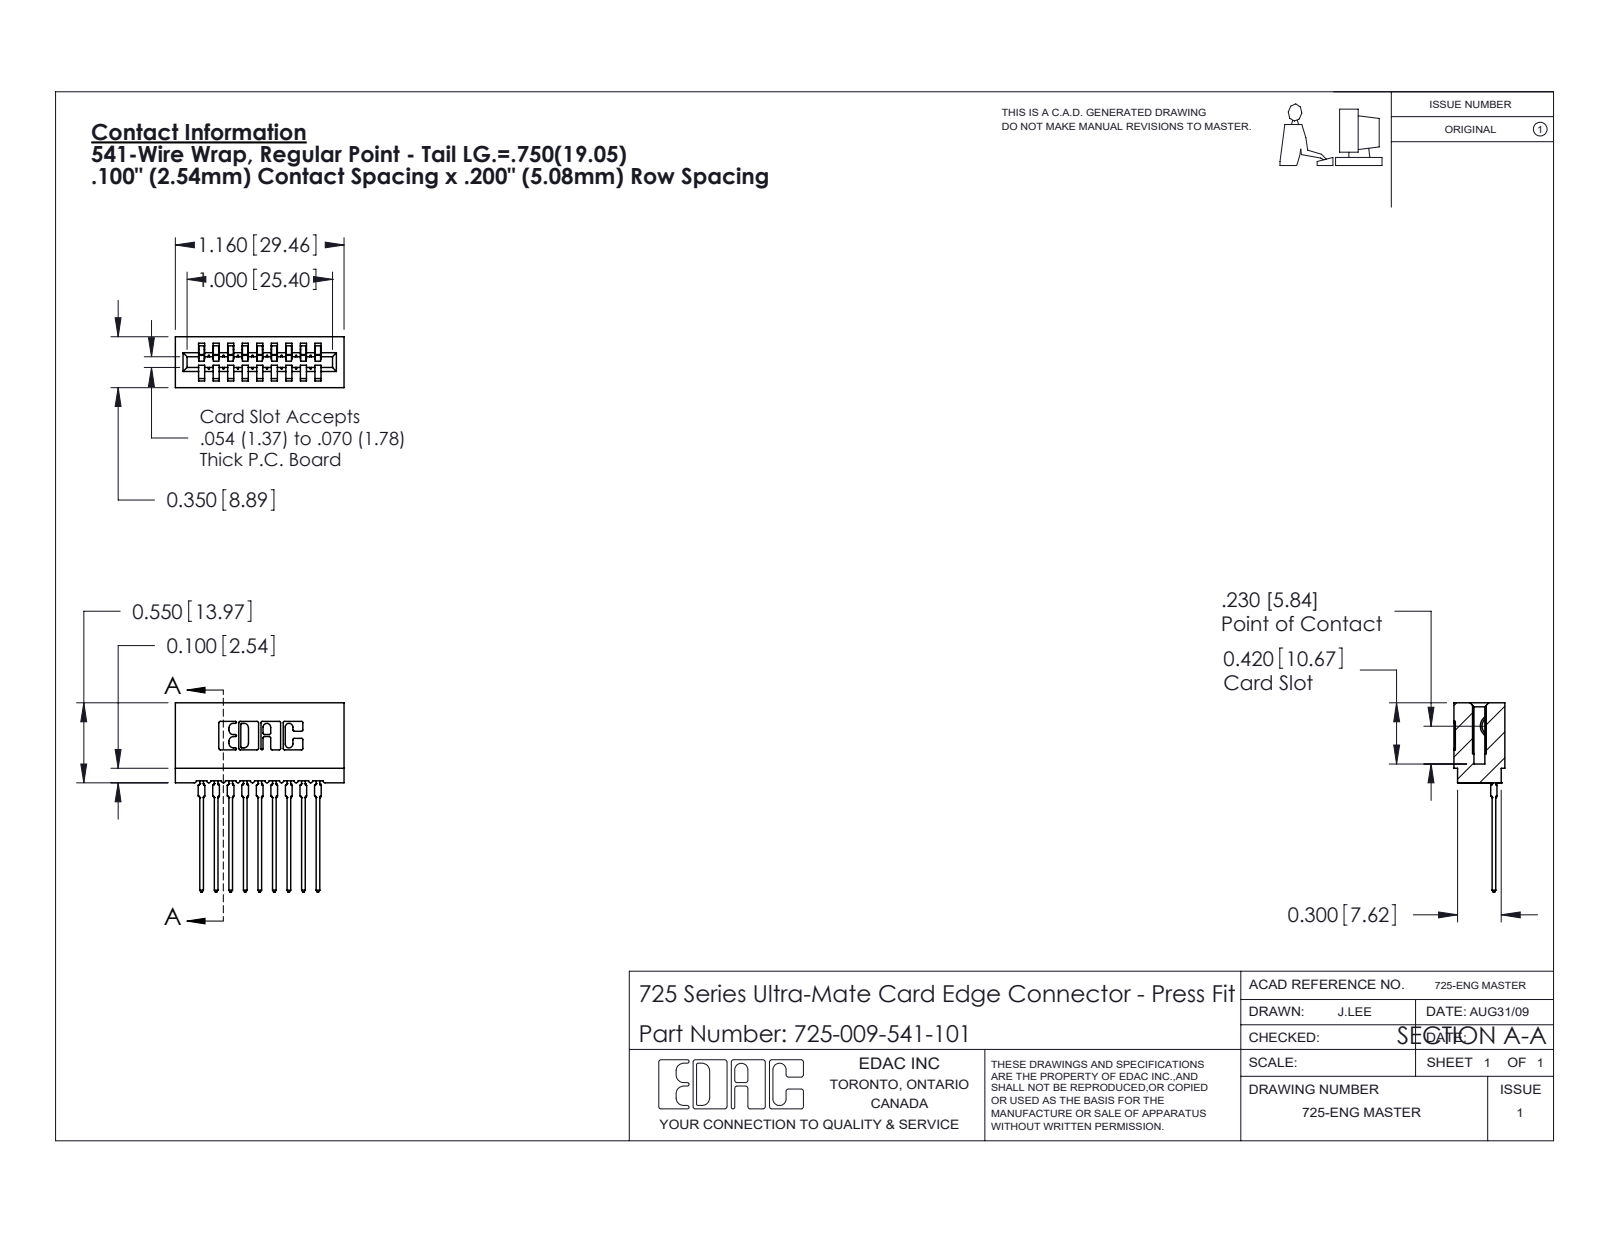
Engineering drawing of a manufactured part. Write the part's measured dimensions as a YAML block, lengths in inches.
part_name: "745-292-001_541; 725 Part_Insulator Option - 01; 725-009-541-101"
step_written_by: "SolidWorks 2020 (CONFIG_CONTROL_DESIGN)"
units: inches
bodies: {solids: 10, faces: 1103, planar: 658, cylindrical: 211, other: 234}
overall_size: [1.301, 1.16, 0.35]
volume: 0.15
surface_area: 6.68
partial_cylinders:
  - {radius: 0.01, count: 22}
  - {radius: 0.015, count: 18}
  - {radius: 0.021, count: 18}
  - {radius: 0.007, count: 6}
  - {radius: 0.031, count: 6}
  - {radius: 0.005, count: 4}
  - {radius: 0.011, count: 4}
  - {radius: 0.026, count: 3}
face_to_face_distances: [0.1, 0.2, 0.3, 0.4, 0.042, 0.5, 0.142, 0.058, 0.242, 0.158]
